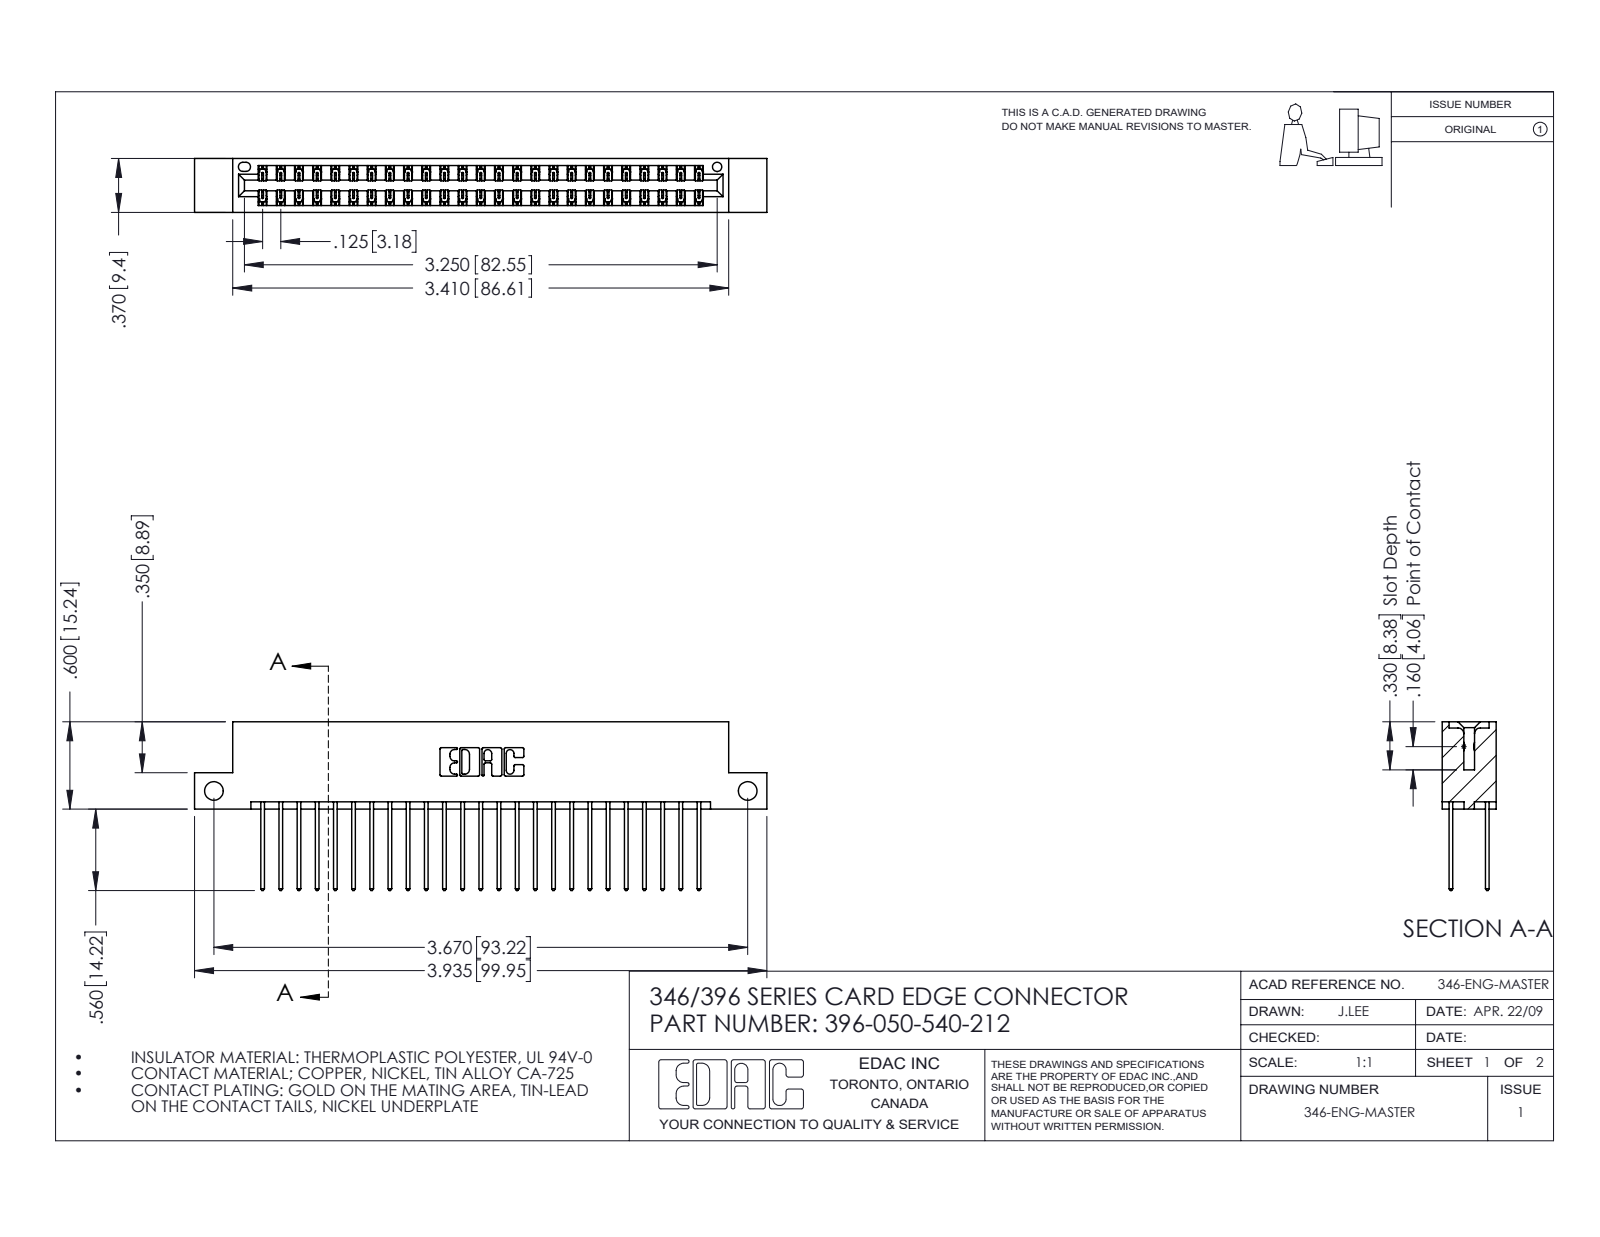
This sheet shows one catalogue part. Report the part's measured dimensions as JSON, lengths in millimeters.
{"part_name": "346 Part_Flush Mounting Lugs - Side Mount; 345-292-001_345-293-140; 396-050-540-212", "step_written_by": "SolidWorks 2016 (CONFIG_CONTROL_DESIGN)", "units": "millimeters", "bodies": {"solids": 51, "faces": 2722, "planar": 1826, "cylindrical": 896, "other": 0}, "overall_size": [99.9, 29.5, 9.4], "volume_mm3": 9720, "surface_area_mm2": 13850, "round_holes": [[3.3, 2], [1.6, 1]], "partial_cylinders_radius": [[0.2, 75], [0.3, 50], [0.3, 22], [0.2, 6], [0.8, 6], [0.7, 3], [0.4, 2], [0.6, 2]], "face_to_face_distances": [1.2, 8.2, 6.4, 1.8, 7.6, 0.6, 9.4, 7, 3.8, 5.6], "hole_center_spacings": [93.2]}
